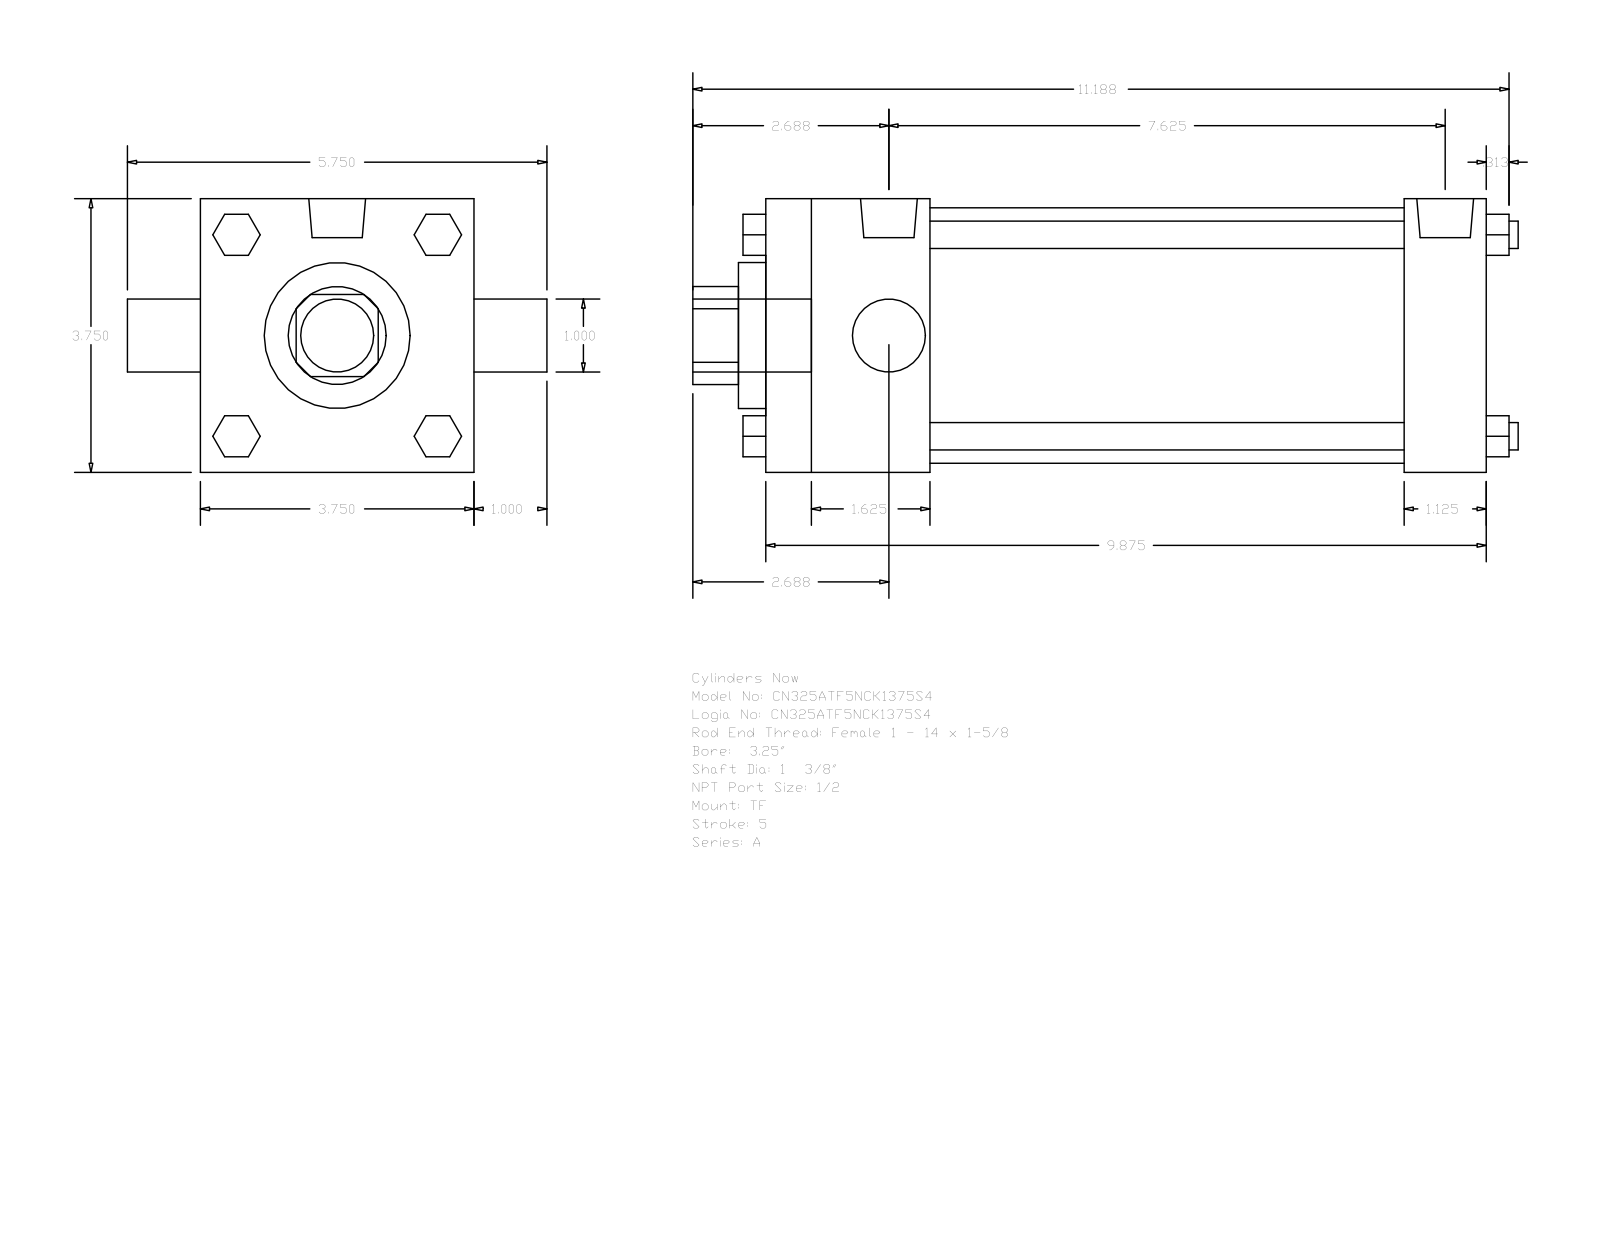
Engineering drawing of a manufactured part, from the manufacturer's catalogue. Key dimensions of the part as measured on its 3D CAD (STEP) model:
Part name (STEP PRODUCT): A_TF__0325_1.375
STEP written by: GSSL Pune (CONFIG_CONTROL_DESIGN)
Units: millimetres
Bodies: 0 solids, 120 faces (92 planar, 28 cylindrical, 0 other)
Overall size (bounding box): 287.34 × 146.05 × 95.25
Round holes (diameter × count): ⌀25.4 ×1, ⌀34.92 ×1, ⌀50.8 ×1, ⌀88.9 ×1
Round bosses / shafts (diameter × count): ⌀9.53 ×4, ⌀8.73 ×3, ⌀19.77 ×2, ⌀25.4 ×1
Partial cylindrical surfaces — rounded edges, fillets, slot ends (radius × count): R17.06 ×1
Main face-to-face distances: 95.24, 250.83, 28.58, 57.15, 222.25, 165.1, 193.68, 9.52, 66.67, 231.77
